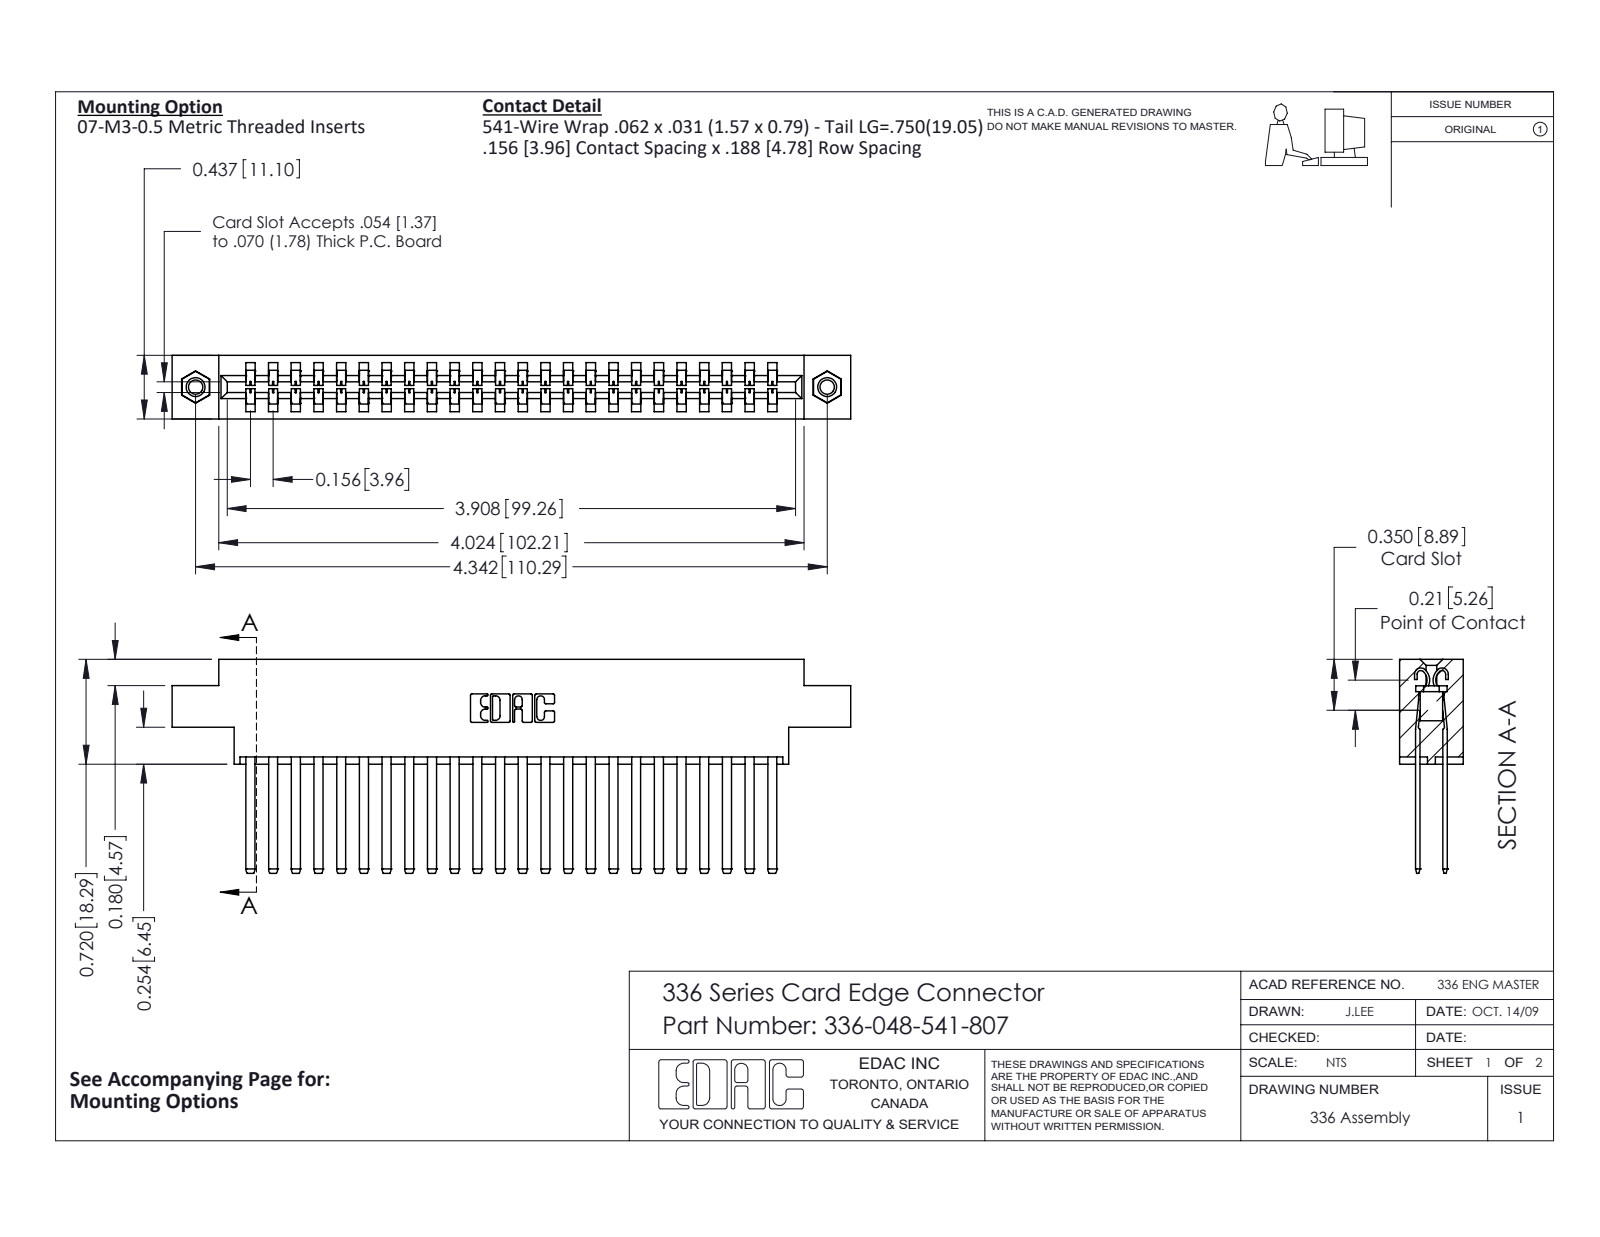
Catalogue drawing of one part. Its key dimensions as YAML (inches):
part_name: "345-250-001_345-250-005-103; 336-290-001_336-290-541; 336 Part_Offset - .156 Dia - TI; 336-048-541-807"
step_written_by: "SolidWorks 2020 (CONFIG_CONTROL_DESIGN)"
units: inches
bodies: {solids: 51, faces: 2194, planar: 1354, cylindrical: 824, other: 16}
overall_size: [4.665, 1.47, 0.437]
volume: 1.08
surface_area: 34.72
round_holes:
  - {diameter: 0.098, count: 2}
  - {diameter: 0.125, count: 2}
  - {diameter: 0.156, count: 2}
round_bosses_or_shafts:
  - {diameter: 0.155, count: 2}
partial_cylinders:
  - {radius: 0.004, count: 96}
  - {radius: 0.056, count: 48}
  - {radius: 0.01, count: 22}
  - {radius: 0.007, count: 6}
  - {radius: 0.031, count: 6}
  - {radius: 0.022, count: 4}
  - {radius: 0.04, count: 4}
  - {radius: 0.026, count: 3}
face_to_face_distances: [0.188, 0.328, 0.14, 0.297, 0.109, 0.031, 0.437, 0.033, 0.181, 0.156]
hole_center_spacings: [4.342]
